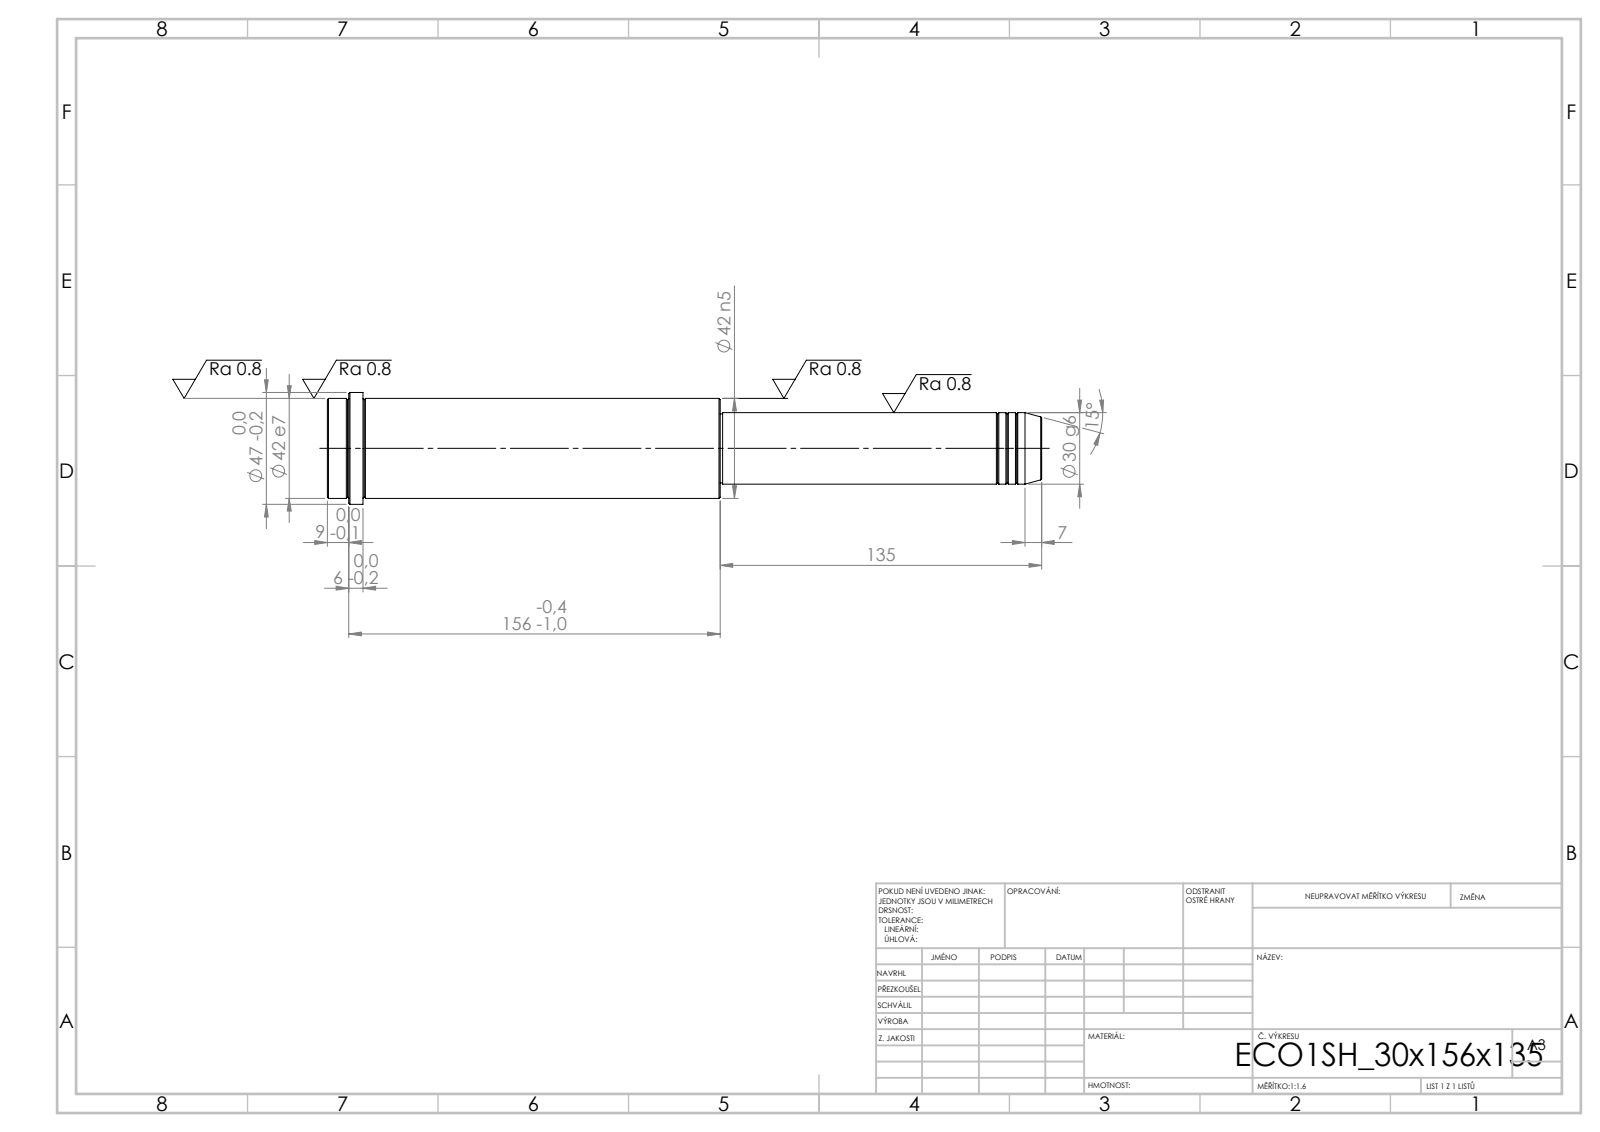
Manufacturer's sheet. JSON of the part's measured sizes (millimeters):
{"step_written_by": "SolidWorks 2019 (CONFIG_CONTROL_DESIGN)", "units": "millimeters", "bodies": {"solids": 1, "faces": 52, "planar": 6, "cylindrical": 16, "other": 30}, "overall_size": [300, 47, 47], "volume_mm3": 325216, "surface_area_mm2": 38129, "round_bosses_or_shafts": [[47, 1], [42, 1], [30, 1], [29, 1]], "face_to_face_distances": [165, 135, 300, 285, 150, 15, 291, 156, 6, 9]}
